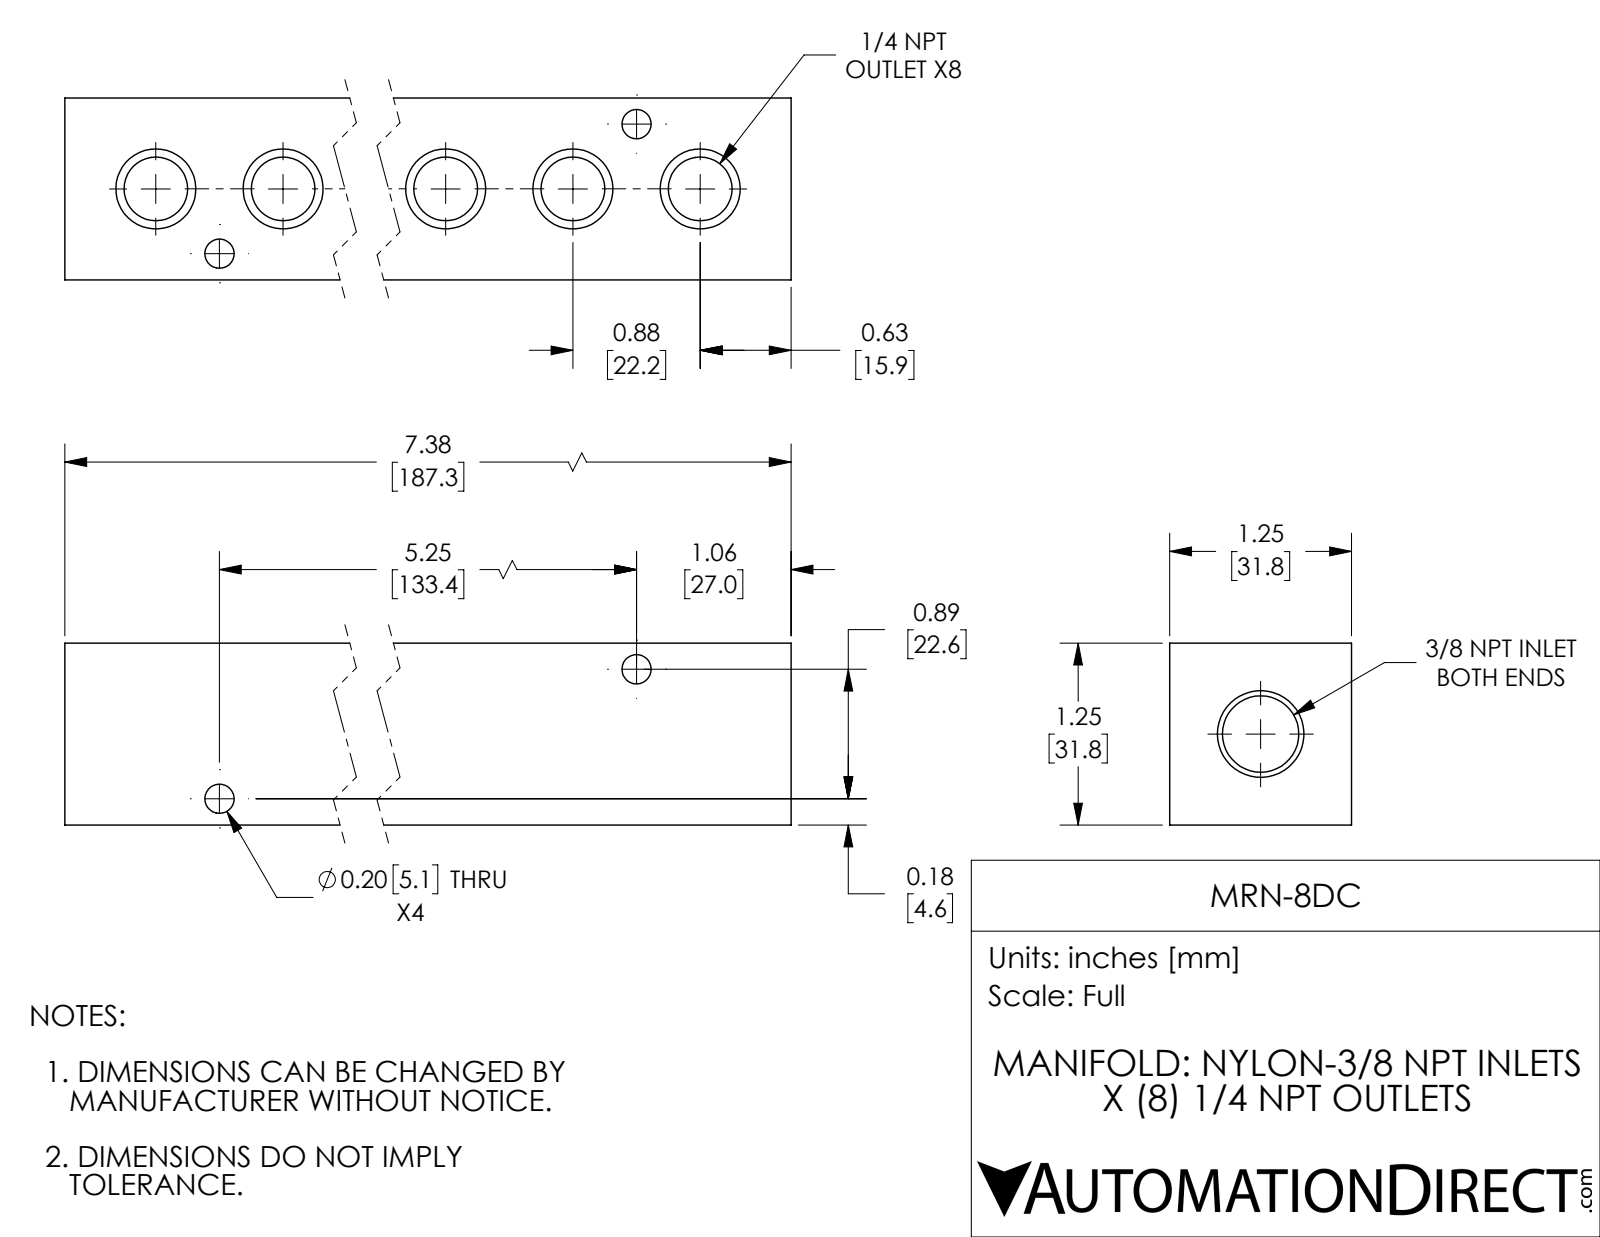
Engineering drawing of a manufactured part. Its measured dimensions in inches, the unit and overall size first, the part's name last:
Units: inches
Overall size (bounding box): 7.375 × 1.25 × 1.25
Round holes (diameter × count): ⌀0.438 ×8, ⌀0.201 ×4, ⌀0.525 ×1
Main face-to-face distances: 1.25, 7.375
Hole centre spacings: 1.75, 0.624, 0.875, 0.875, 2.625, 3.5, 2.625, 4.375
Volume: 9.291 in³ · Surface area: 55.95 in²
Bodies: 1 solid, 60 faces (6 planar, 34 cylindrical, 20 other)
Part name (STEP PRODUCT): MRN-8DC
STEP written by: SolidWorks 2018 (AUTOMOTIVE_DESIGN)
